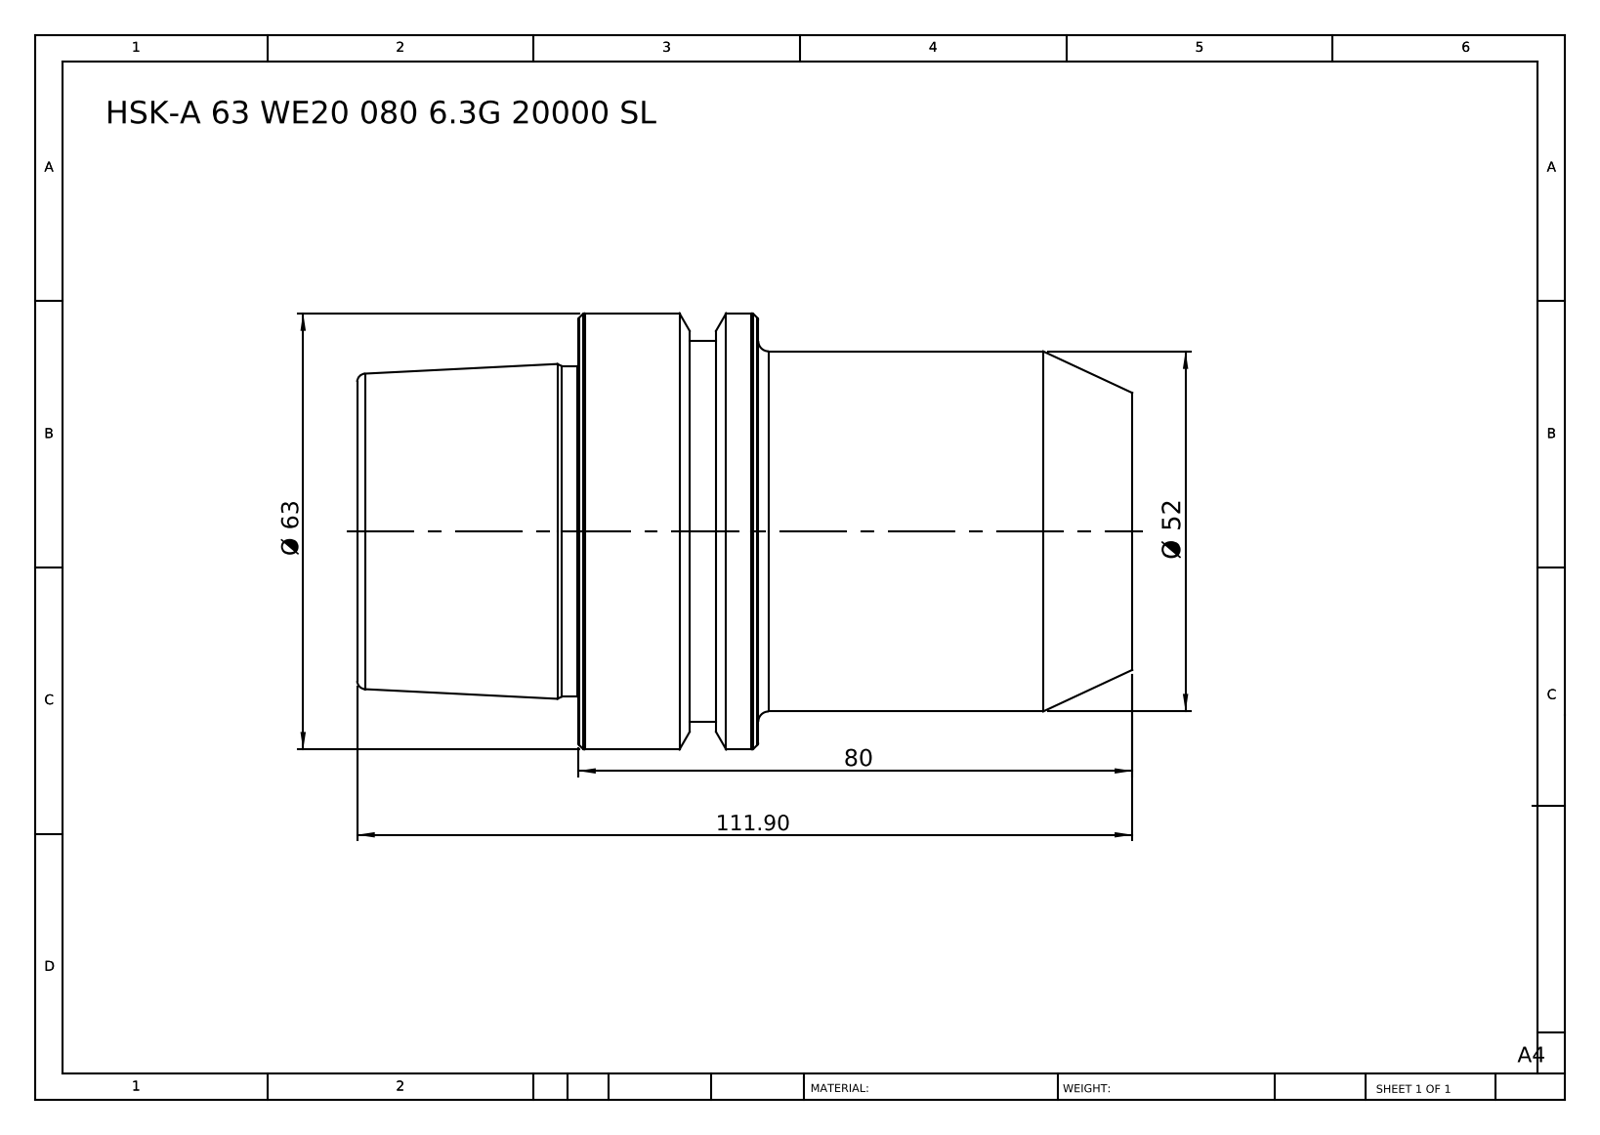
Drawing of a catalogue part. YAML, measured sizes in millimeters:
part_name: "HSK-A 63 WE20 080 6.3G 20000 SL"
step_written_by: "SolidWorks 2014 (CONFIG_CONTROL_DESIGN)"
units: millimeters
bodies: {solids: 1, faces: 46, planar: 6, cylindrical: 10, other: 30}
overall_size: [111.9, 63, 63]
volume: 241511
surface_area: 24447
round_bosses_or_shafts:
  - {diameter: 63, count: 1}
  - {diameter: 55, count: 1}
  - {diameter: 52, count: 1}
  - {diameter: 47.78, count: 1}
face_to_face_distances: [111.9, 80, 31.9, 54, 26, 57.9, 60.1, 6.1, 19.9, 51.8]
